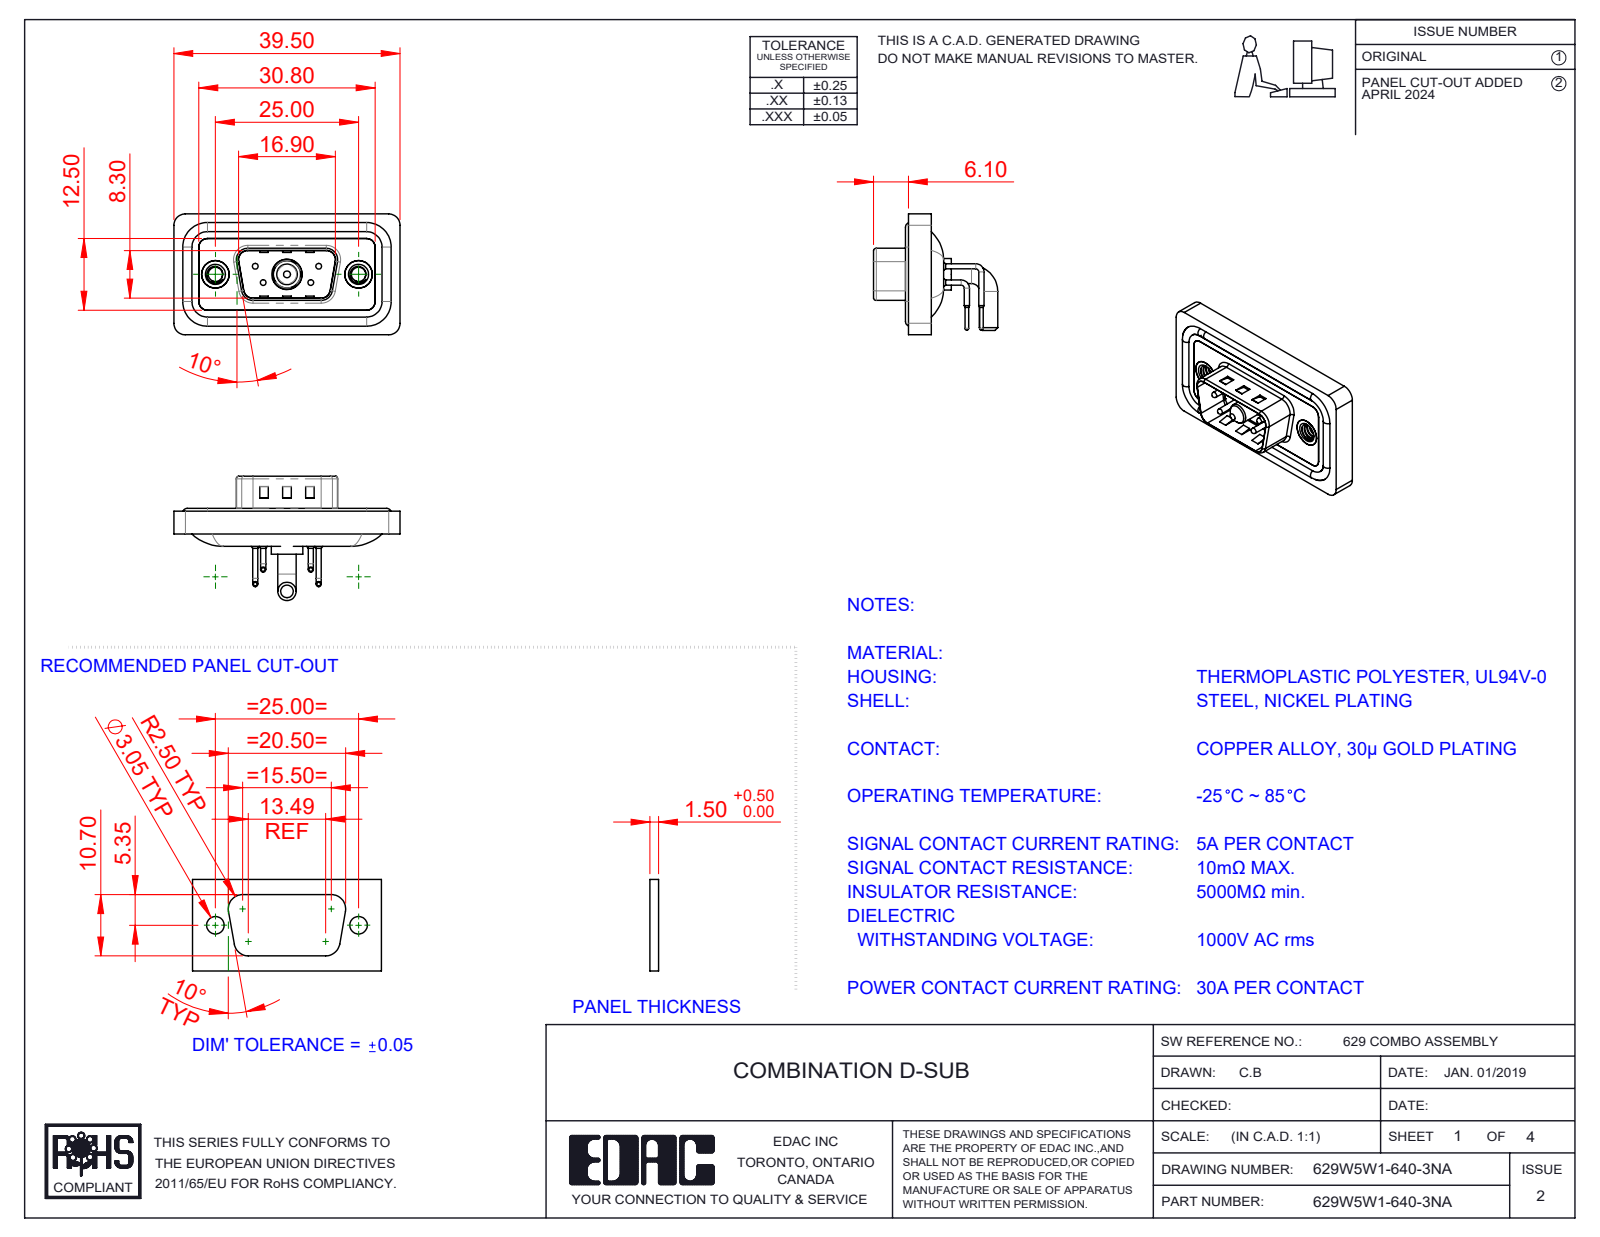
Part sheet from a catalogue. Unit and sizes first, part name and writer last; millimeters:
Units: millimetres
Overall size (bounding box): 39.5 × 21.7 × 21.1
Round holes (diameter × count): ⌀0.75 ×4, ⌀1.6 ×4, ⌀2 ×4, ⌀2.5 ×2, ⌀4 ×2, ⌀4.8 ×2, ⌀5 ×2, ⌀4.85 ×1, ⌀5.3 ×1
Round bosses / shafts (diameter × count): ⌀0.9 ×8, ⌀1.6 ×4, ⌀1.5 ×4, ⌀1 ×4, ⌀0.65 ×4, ⌀4.9 ×2, ⌀3.2 ×2, ⌀5.5 ×1
Partial cylindrical surfaces — rounded edges, fillets, slot ends (radius × count): R1.5 ×18, R2 ×18, R0.5 ×8, R1.6 ×8, R0.25 ×4, R0.6 ×4, R0.65 ×4, R0.9 ×4
Main face-to-face distances: 0.4, 2.9, 1.1, 0.8, 2.1, 2.5, 1.6, 3.1, 4.5, 1.5
Hole centre spacings: 3.16, 5.72, 7.1, 12.5, 18.1, 4.39, 4.4, 8.31
Volume: 4 508 mm³ · Surface area: 7 186 mm²
Bodies: 13 solids, 888 faces (411 planar, 343 cylindrical, 134 other)
Part name (STEP PRODUCT): Power Pin_30A RA; 629Combo Contact Row 1; 629Combo Shell Front_09 Contacts; 629Combo Shell Rear_09 Contacts (+5 more)
STEP written by: SolidWorks 2023 (CONFIG_CONTROL_DESIGN)
